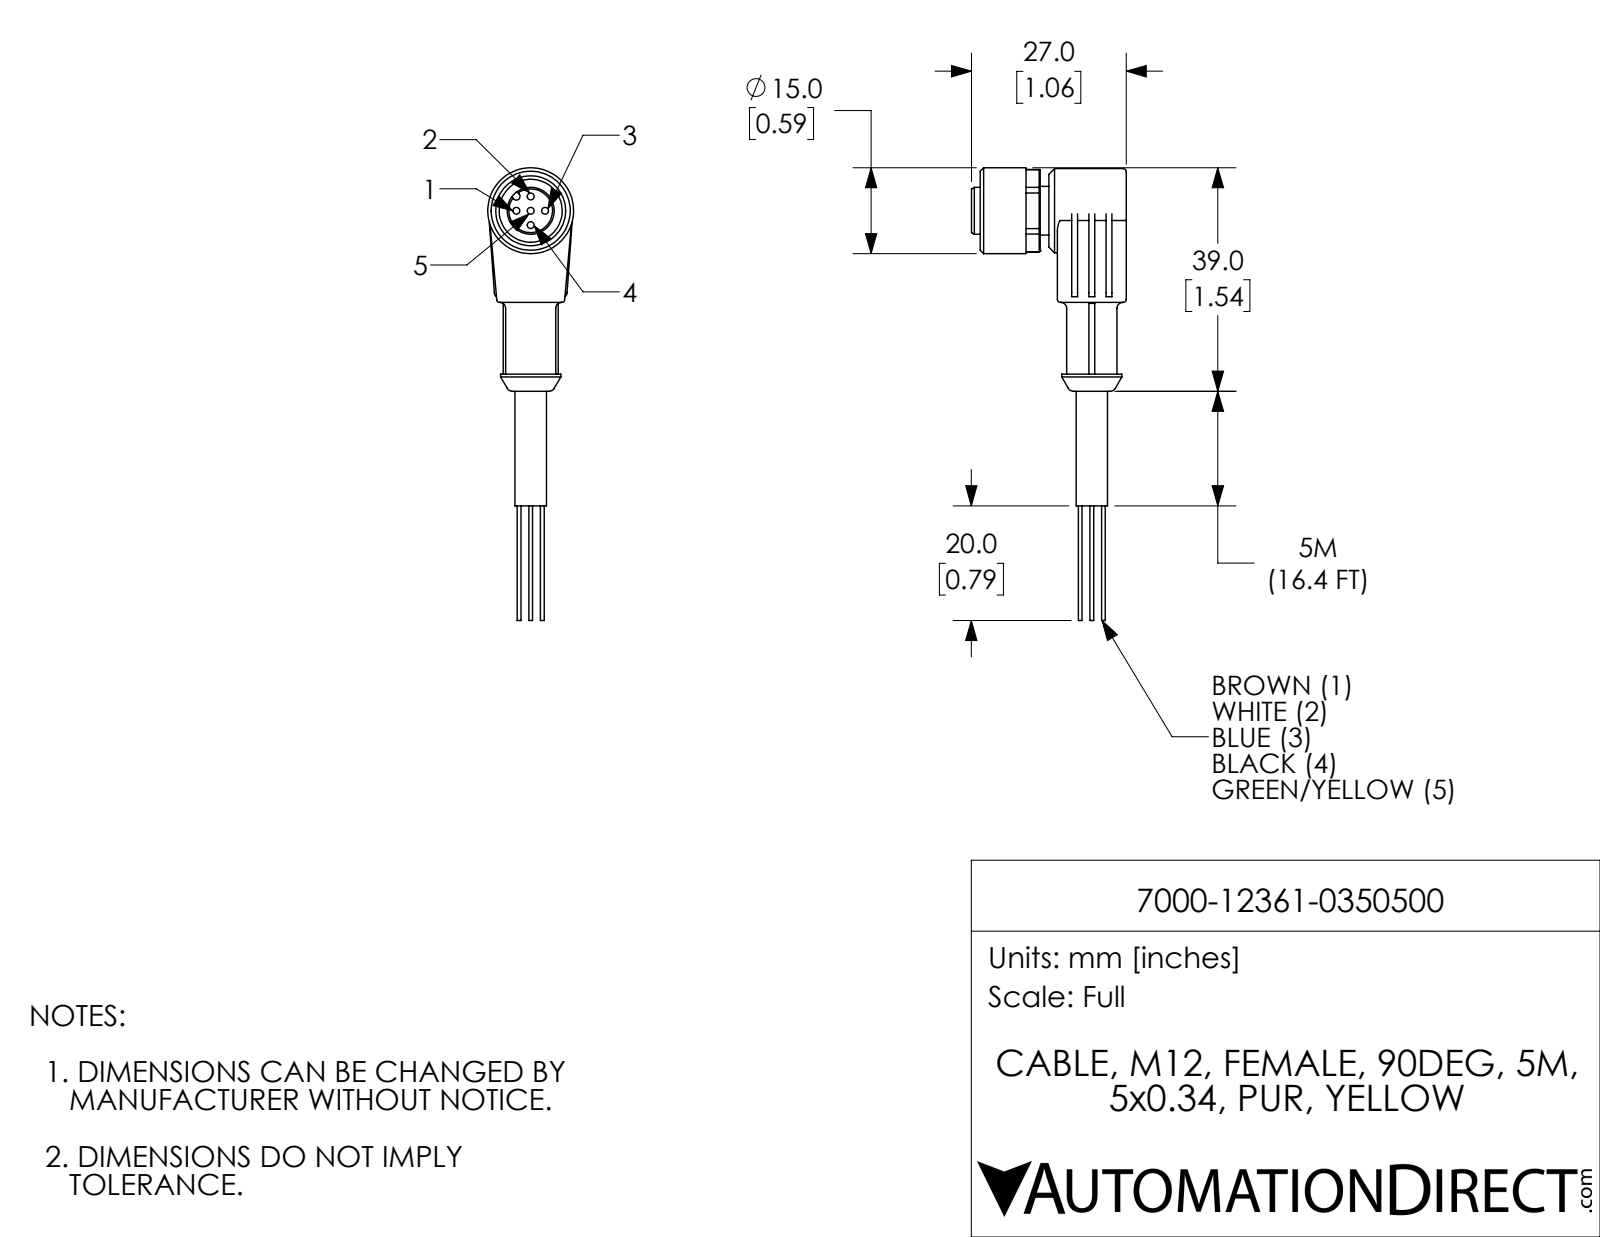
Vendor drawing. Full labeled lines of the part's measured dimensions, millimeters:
Part name (STEP PRODUCT): 7000-12361-0350500
STEP written by: SolidWorks 2021 (CONFIG_CONTROL_DESIGN)
Units: millimetres
Bodies: 1 solid, 155 faces (66 planar, 61 cylindrical, 28 other)
Overall size (bounding box): 79 × 27 × 15
Volume: 6 830 mm³ · Surface area: 3 817 mm²
Round holes (diameter × count): ⌀1.2 ×5, ⌀4.8 ×1, ⌀11 ×1
Round bosses / shafts (diameter × count): ⌀0.7 ×5, ⌀15 ×1, ⌀14.7 ×1, ⌀10.5 ×1, ⌀8.8 ×1, ⌀8.5 ×1, ⌀8.2 ×1, ⌀5.5 ×1
Partial cylindrical surfaces — rounded edges, fillets, slot ends (radius × count): R0.5 ×8, R1 ×2, R0.7 ×1, R7.2 ×1
Main face-to-face distances: 12, 1.5, 3, 13.5, 15, 5.5, 9.5, 6, 8, 12.5
Hole centre spacings: 2.5, 3.5, 5
